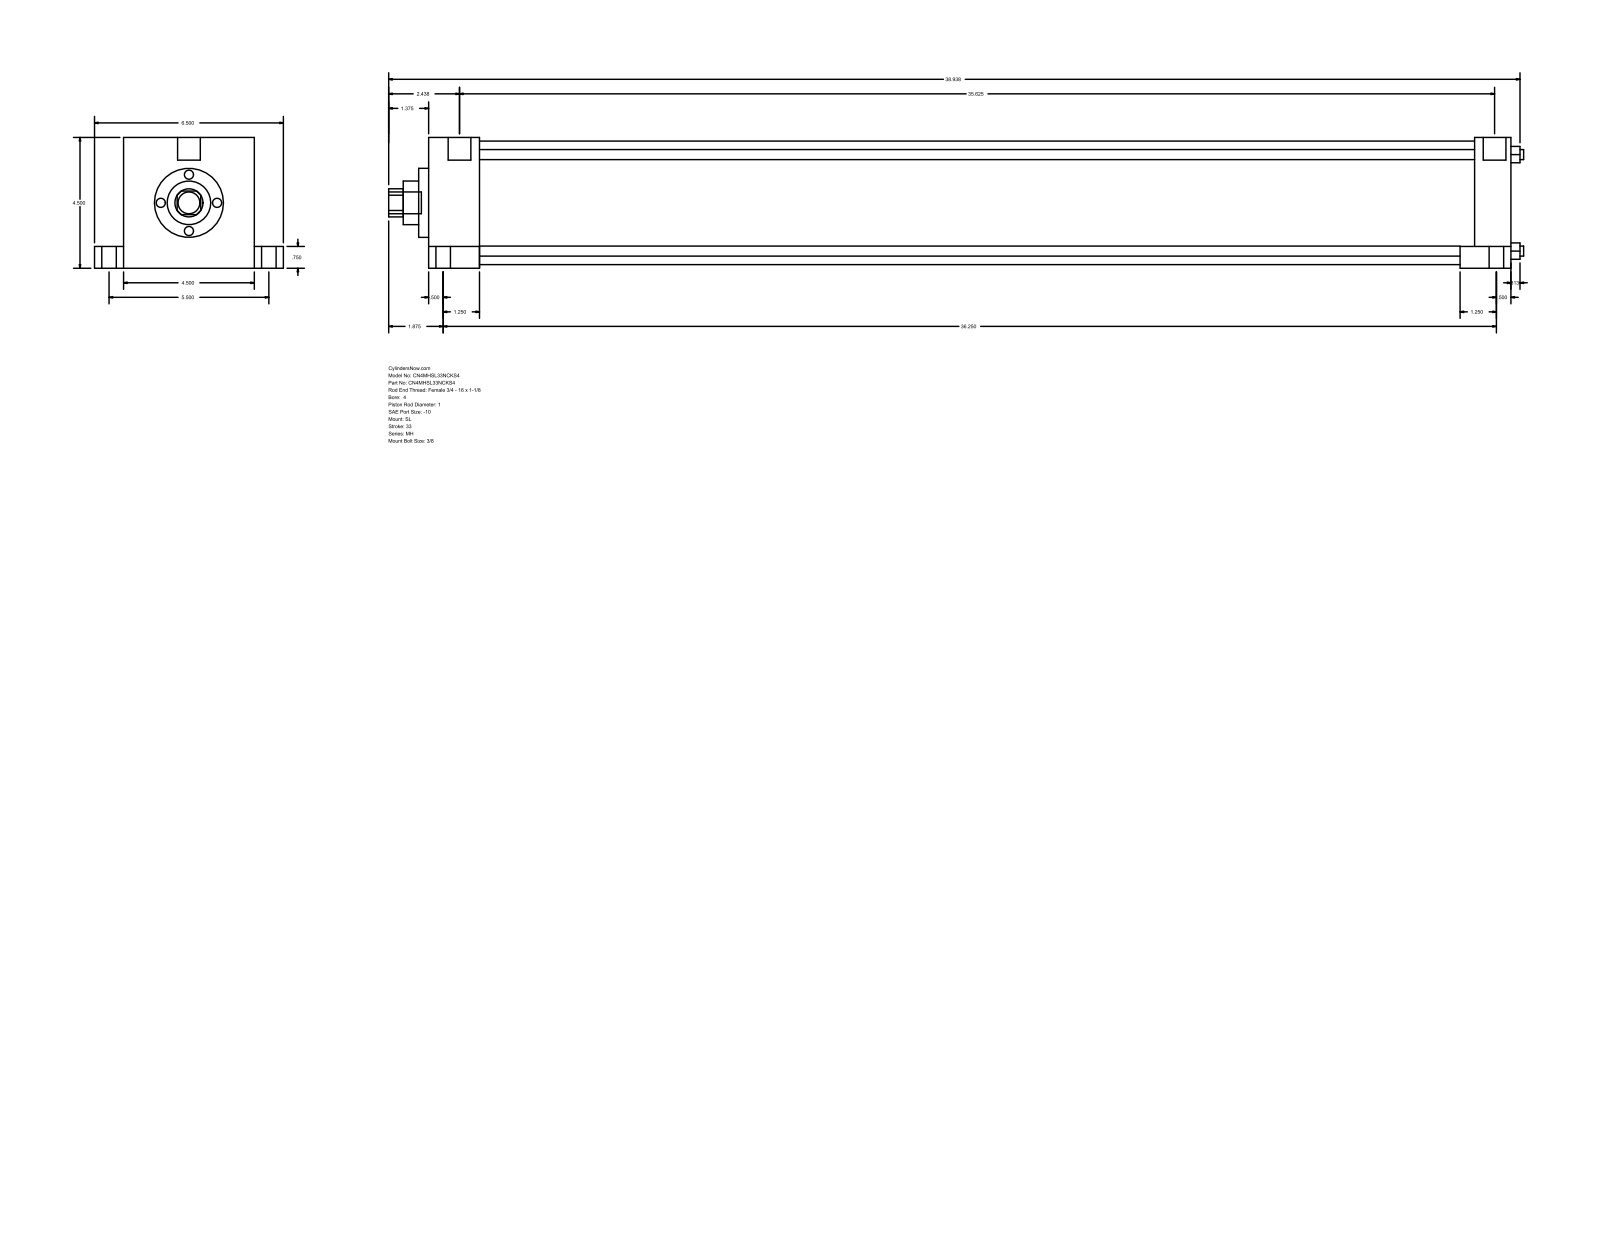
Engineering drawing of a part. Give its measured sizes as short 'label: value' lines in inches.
name: MH_SL__0400_1
written by: GSSL Pune (CONFIG_CONTROL_DESIGN)
unit: in
bodies: 0 solids, 110 faces (77 planar, 33 cylindrical, 0 other)
size: 39.063 × 6.5 × 4.5
holes: 4× ⌀0.345, 1× ⌀1, 1× ⌀1.5, 1× ⌀2.375, 1× ⌀4.25
bosses: 5× ⌀0.75, 4× ⌀0.5, 4× ⌀0.344, 2× ⌀0.781
rounds: 1× R0.484
face distances: 4.5, 37.25, 1.75, 35.5, 36, 34.25, 1.25, 1, 5.5, 0.75
hole spacings: 2.347, 3.32, 4.695
